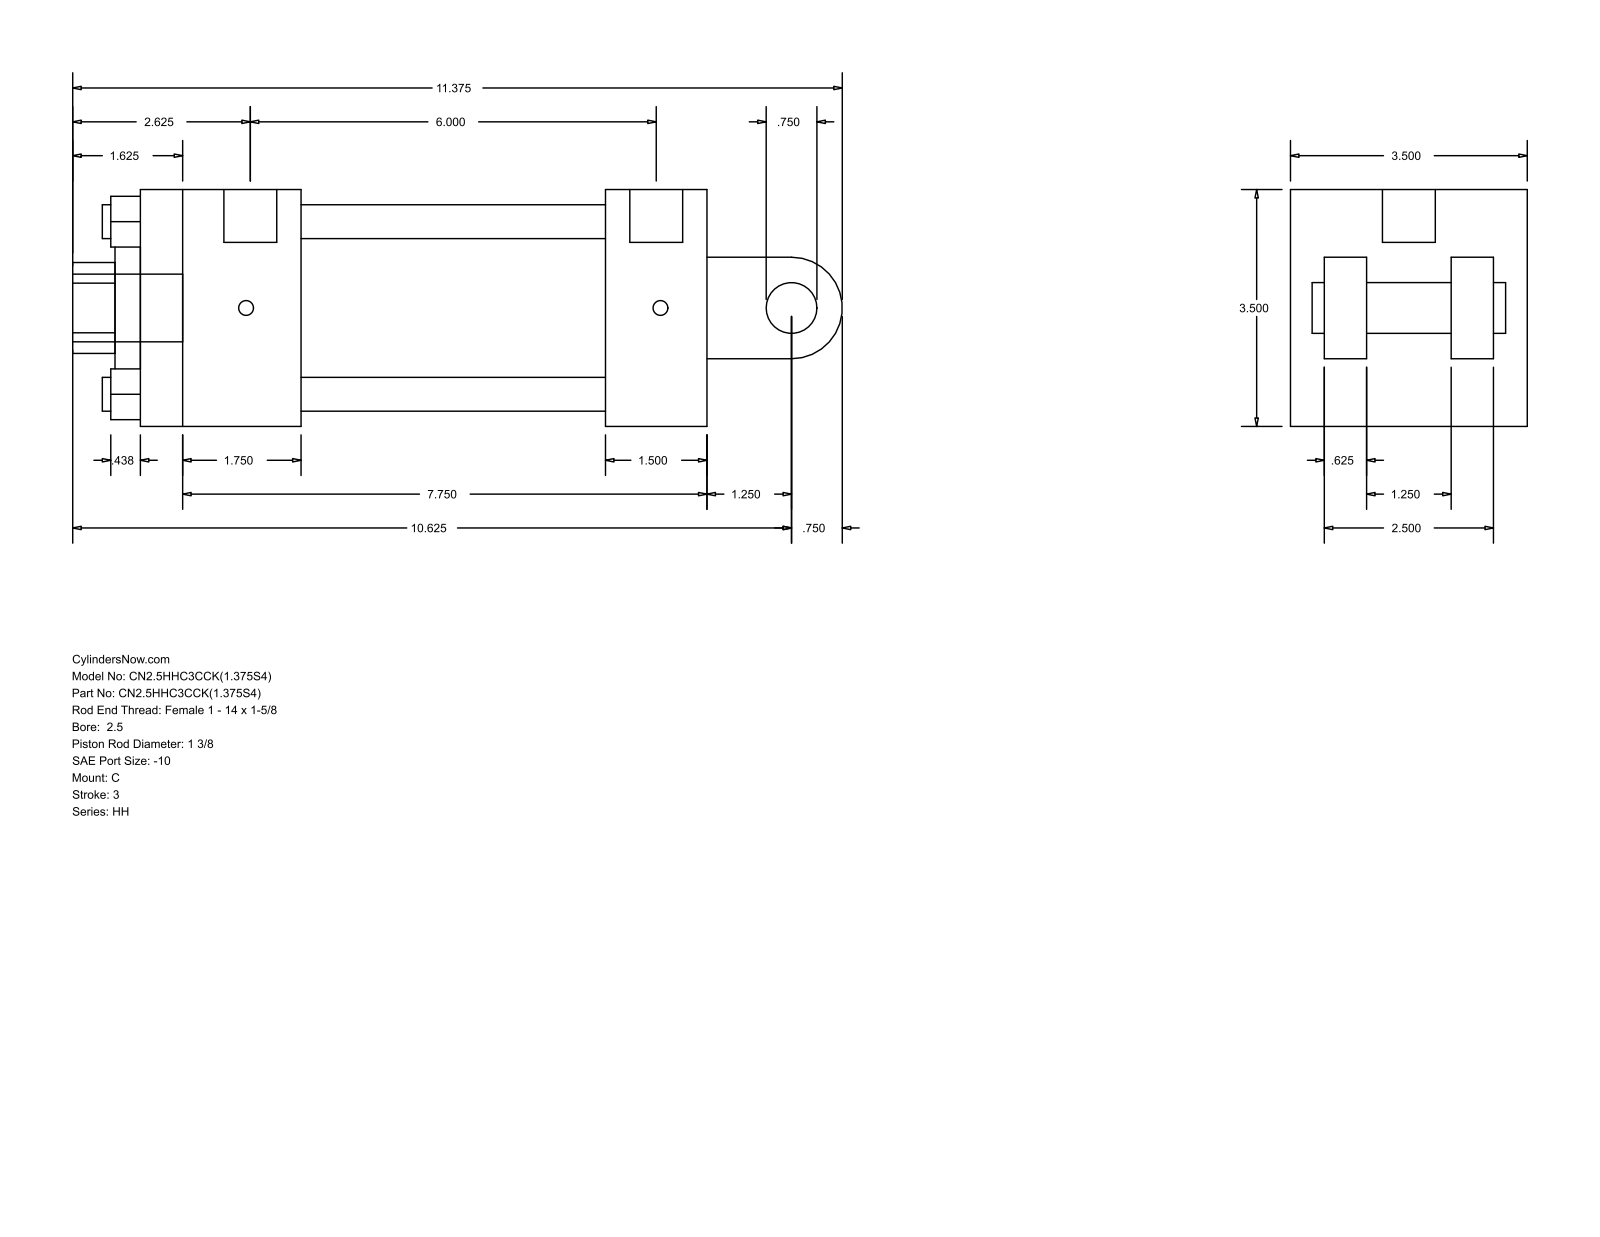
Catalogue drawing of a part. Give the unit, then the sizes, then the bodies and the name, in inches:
Units: inches
Overall size (bounding box): 11.375 × 3.5 × 3.5
Round holes (diameter × count): ⌀0.5 ×4, ⌀0.219 ×2, ⌀0.781 ×1, ⌀1.375 ×1, ⌀2 ×1, ⌀2.875 ×1
Round bosses / shafts (diameter × count): ⌀0.219 ×2, ⌀1 ×1, ⌀0.781 ×1, ⌀0.75 ×1
Partial cylindrical surfaces — rounded edges, fillets, slot ends (radius × count): R0.672 ×1, R0.75 ×1
Main face-to-face distances: 3.5, 8.375, 2.5, 0.625, 0.5, 6.875, 1.5, 2.375, 4.5, 6
Hole centre spacings: 1.803, 2.55, 3.606, 0.063
Bodies: 0 solids, 99 faces (70 planar, 29 cylindrical, 0 other)
Part name (STEP PRODUCT): HH_C__0250_1.375
STEP written by: GSSL Pune (CONFIG_CONTROL_DESIGN)
